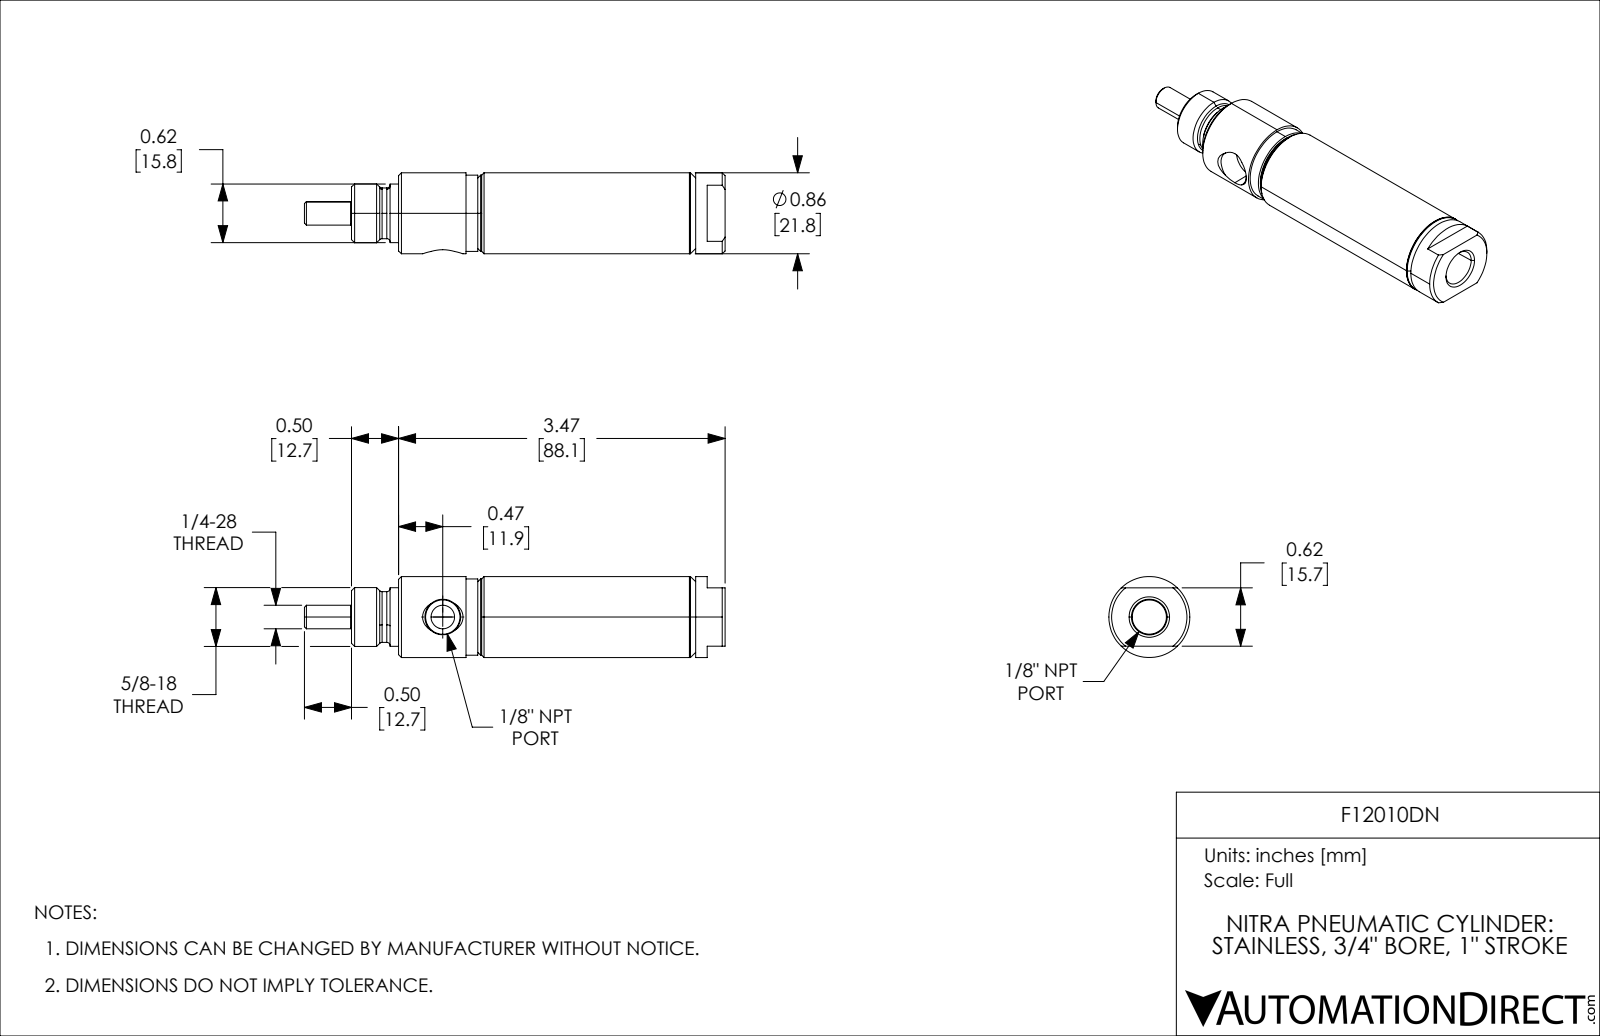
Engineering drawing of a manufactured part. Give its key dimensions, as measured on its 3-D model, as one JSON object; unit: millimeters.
{"part_name": "F12010DN_3; F12010DN_9; F12010DN_5; F12010DN (+1 more)", "step_written_by": "SolidWorks 2021 (CONFIG_CONTROL_DESIGN)", "units": "millimeters", "bodies": {"solids": 4, "faces": 124, "planar": 22, "cylindrical": 46, "other": 56}, "overall_size": [113.51, 21.84, 21.84], "volume_mm3": 26383, "surface_area_mm2": 17718, "round_holes": [[6.35, 1], [6.95, 1], [12.7, 1], [17.83, 1]], "round_bosses_or_shafts": [[21.84, 1], [20.57, 1], [19.35, 1], [15.88, 1], [15.81, 1], [13.68, 1], [6.35, 1], [5.84, 1]], "face_to_face_distances": [21.43, 25.4, 46.83, 60.32, 34.92, 13.49, 53.19, 12.7, 27.79, 74.62]}
